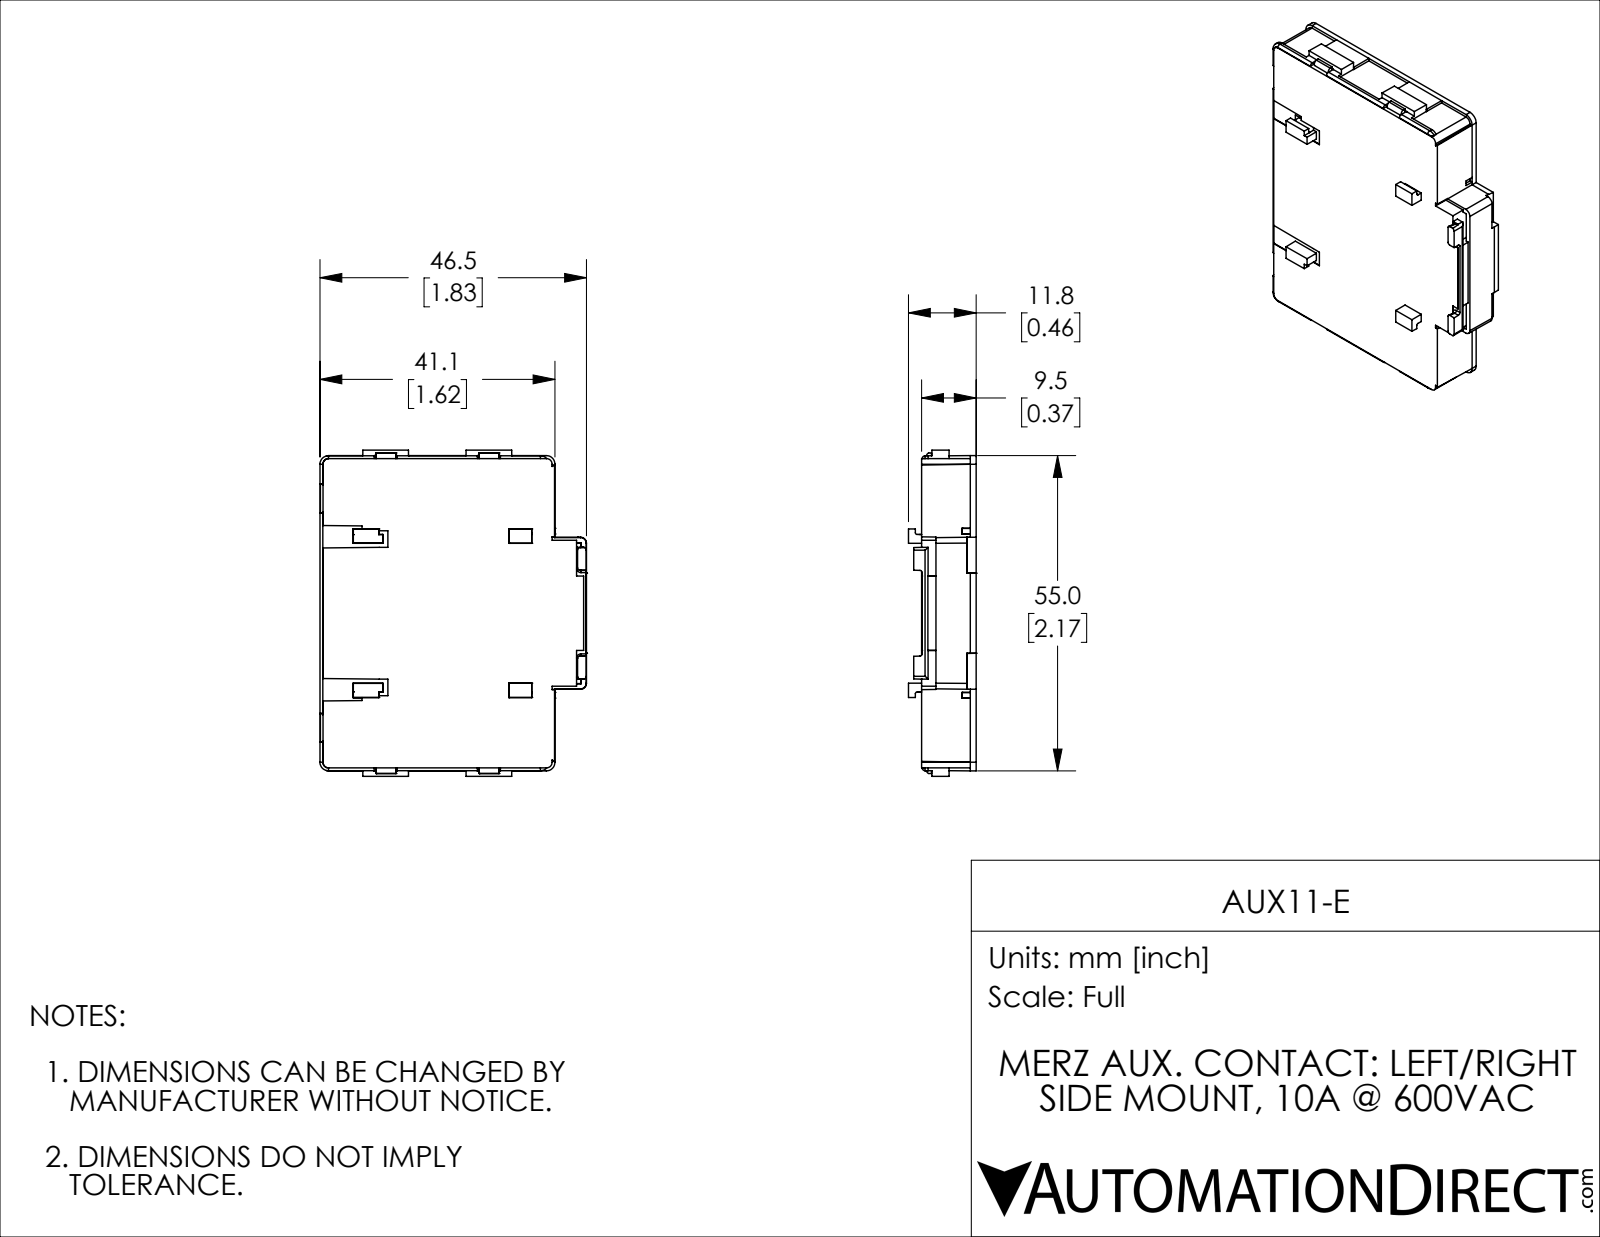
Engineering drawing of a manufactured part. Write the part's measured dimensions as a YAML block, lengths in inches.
part_name: "AUX11-E"
step_written_by: "SolidWorks 2019 (AUTOMOTIVE_DESIGN)"
units: inches
bodies: {solids: 1, faces: 379, planar: 313, cylindrical: 40, other: 26}
overall_size: [2.243, 1.833, 0.465]
volume: 1.37
surface_area: 11.76
partial_cylinders:
  - {radius: 0.016, count: 7}
  - {radius: 0.02, count: 6}
  - {radius: 0.039, count: 6}
  - {radius: 0.012, count: 4}
  - {radius: 0.031, count: 2}
face_to_face_distances: [0.374, 0.039, 0.217, 2.126, 0.335, 0.331, 0.043, 2.202, 0.185, 0.561]
